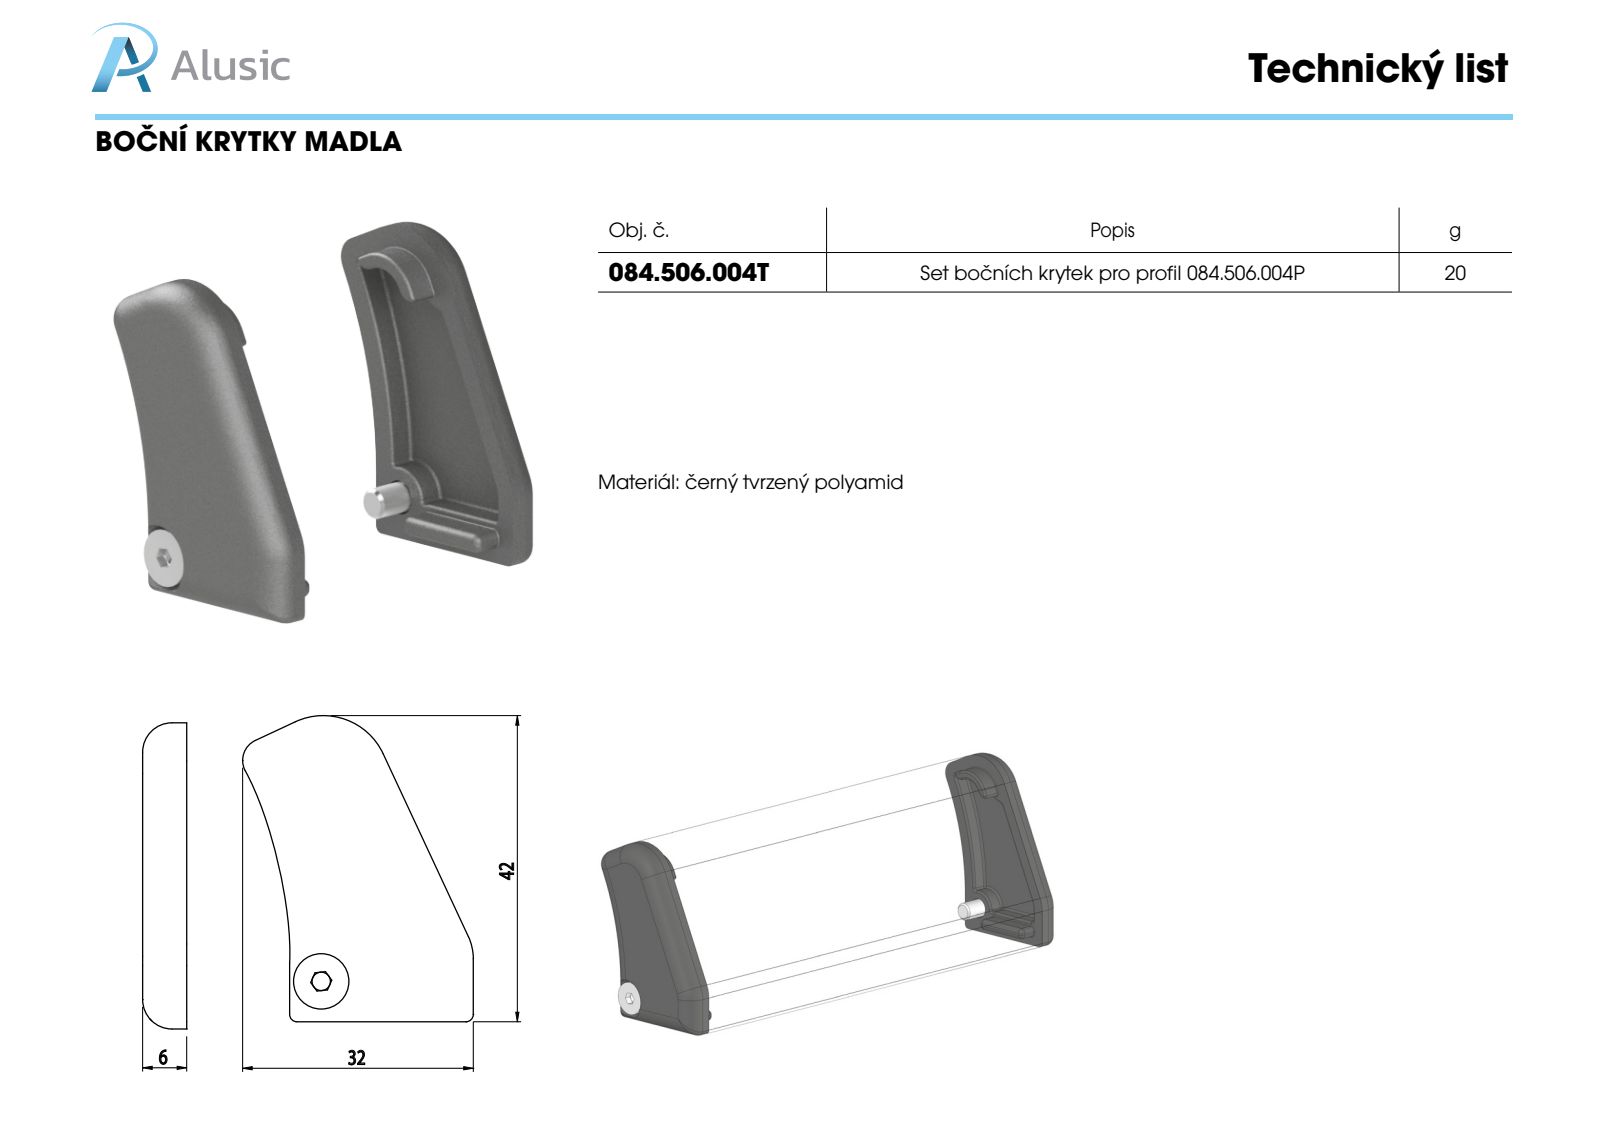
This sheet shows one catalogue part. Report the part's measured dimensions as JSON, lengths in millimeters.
{"part_name": "084.506.004T SX; 084.506.004T; ISO 10642 - M4 x 10 --- 10S_ISO 10642 - M4 x 10 --- 10S; 084.506.004T DX", "step_written_by": "SolidWorks 2016 (CONFIG_CONTROL_DESIGN)", "units": "millimeters", "bodies": {"solids": 4, "faces": 438, "planar": 70, "cylindrical": 158, "other": 210}, "overall_size": [46.14, 45.42, 27.61], "volume_mm3": 7132, "surface_area_mm2": 6119, "round_holes": [[4.5, 2]], "round_bosses_or_shafts": [[7.53, 2], [4, 2]], "partial_cylinders_radius": [[0.5, 40], [4, 16], [0.2, 12], [1, 12], [1.06, 8], [2, 4], [2.06, 4], [3, 2]], "face_to_face_distances": [6, 2.5, 2.51, 3.5, 3.49, 3, 1, 1.5, 4.5, 2]}
